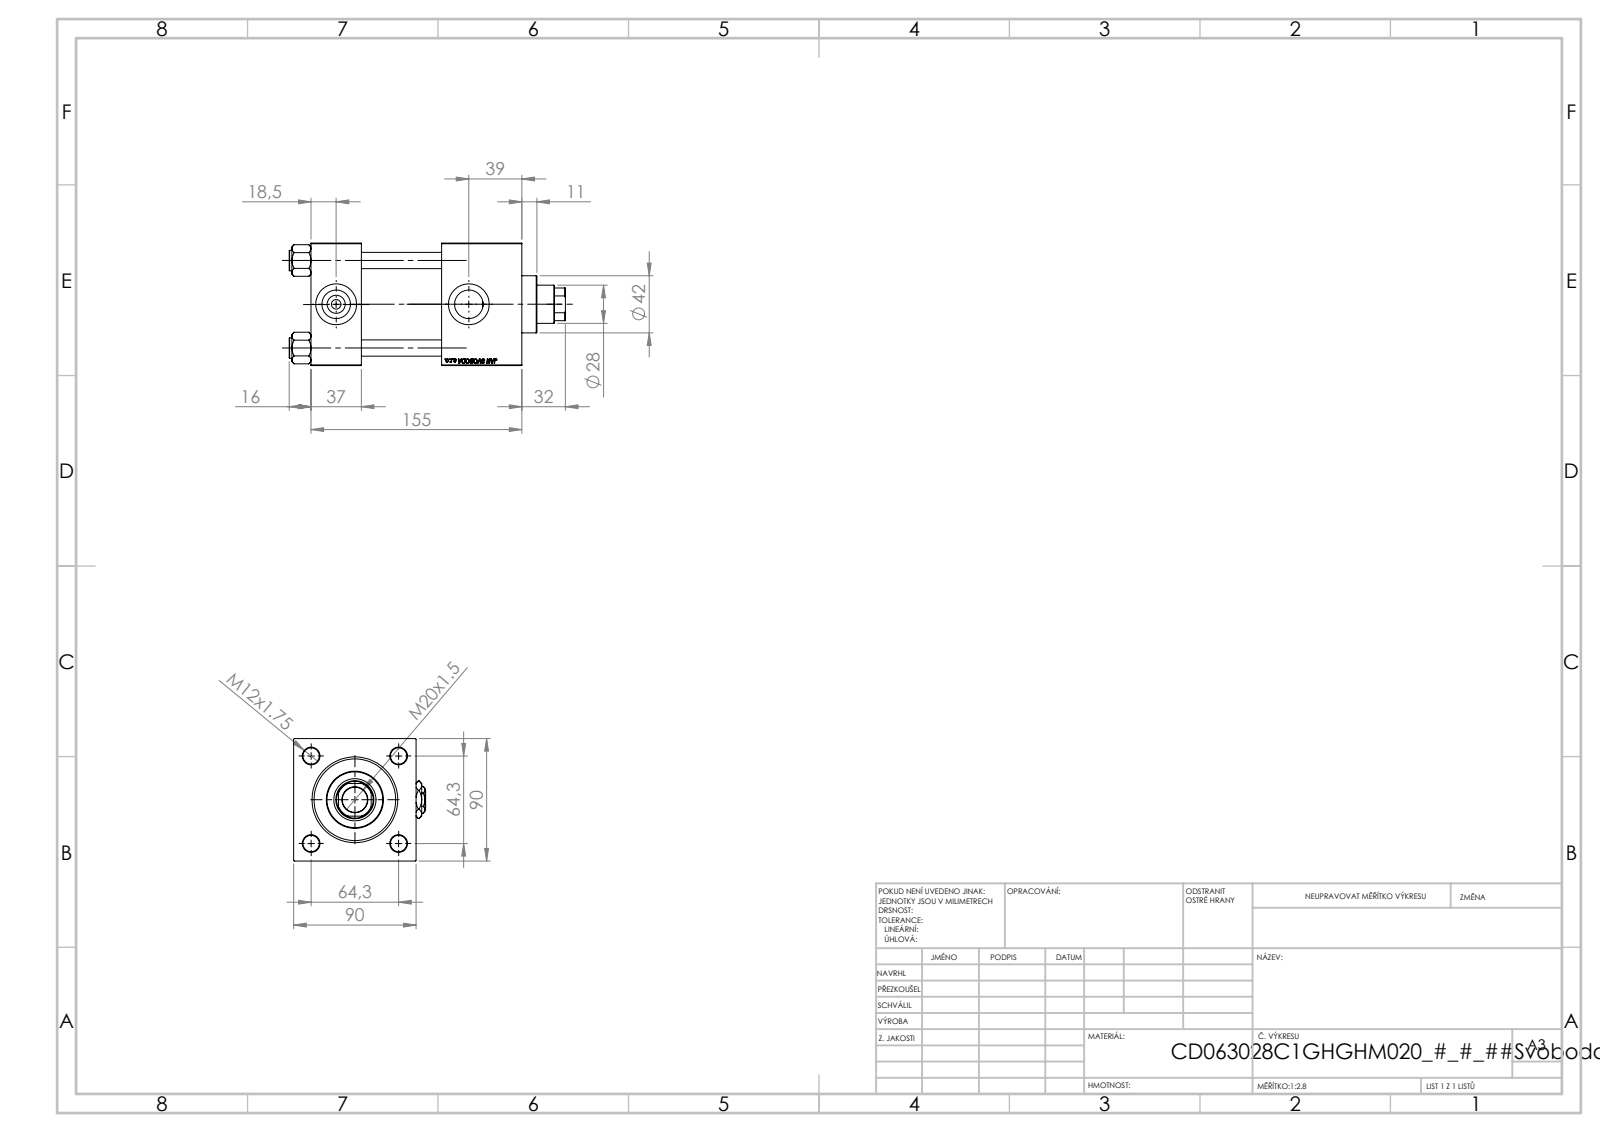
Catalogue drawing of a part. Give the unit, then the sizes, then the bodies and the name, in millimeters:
Units: millimetres
Overall size (bounding box): 203 × 97 × 90
Round holes (diameter × count): ⌀12 ×4, ⌀7 ×2, ⌀20.96 ×2, ⌀30 ×2, ⌀18.5 ×1, ⌀28 ×1, ⌀31 ×1, ⌀50 ×1, ⌀60 ×1, ⌀63 ×1
Round bosses / shafts (diameter × count): ⌀15 ×4, ⌀69 ×1, ⌀42 ×1
Partial cylindrical surfaces — rounded edges, fillets, slot ends (radius × count): R13.5 ×1
Main face-to-face distances: 90, 59, 37, 118, 155, 96, 126.3, 89.3, 30.3, 28.7
Hole centre spacings: 45.47, 64.3, 90.93, 97.5
Volume: 942 456 mm³ · Surface area: 181 253 mm²
Bodies: 12 solids, 1196 faces (550 planar, 90 cylindrical, 556 other)
Part name (STEP PRODUCT): V215CD_VC_C; V215CD_Body_C; Zatka_pro_OIL_PORT; V215CD_C_TYCINKA (+2 more)
STEP written by: SolidWorks 2019 (CONFIG_CONTROL_DESIGN)
